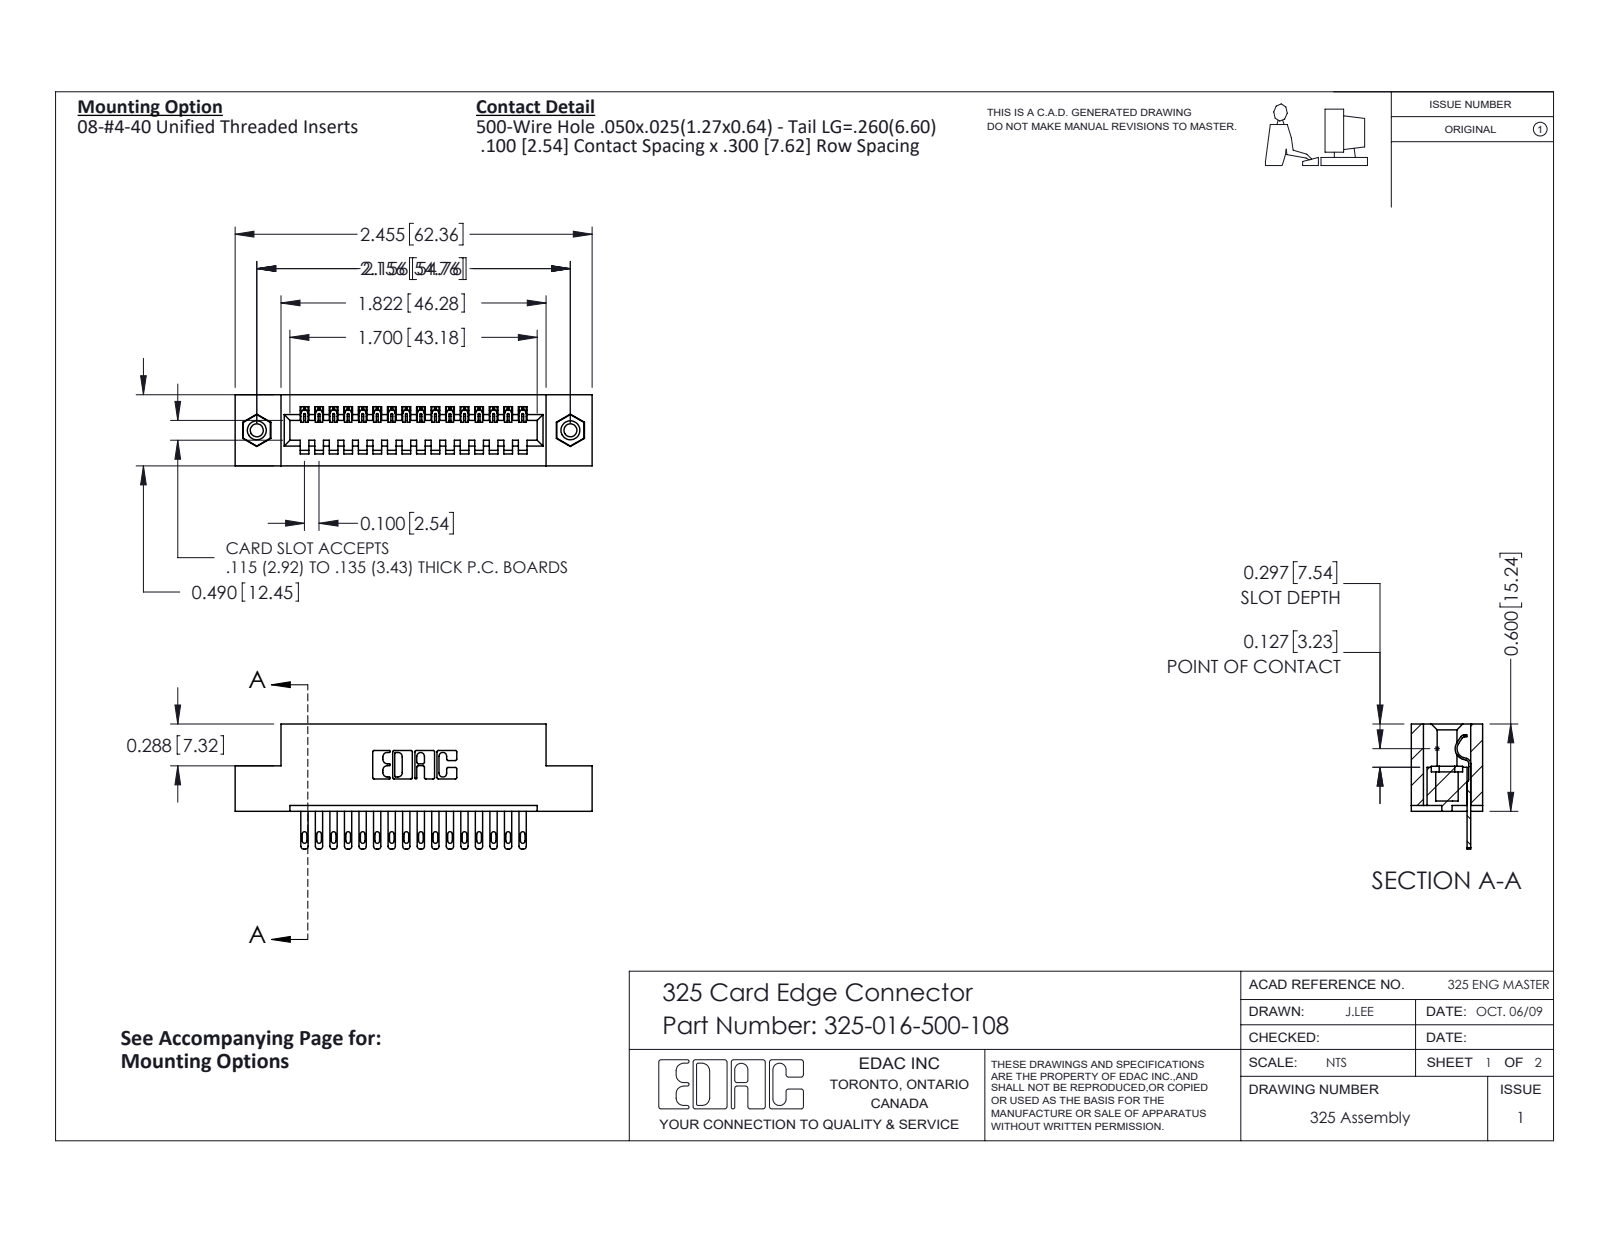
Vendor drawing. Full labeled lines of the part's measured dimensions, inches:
Part name (STEP PRODUCT): 325-016-500-108; 325 Part_TI; 345-250-001_345-250-003-102; 325-292-001_325-293-100
STEP written by: SolidWorks 2016 (CONFIG_CONTROL_DESIGN)
Units: inches
Bodies: 19 solids, 1038 faces (678 planar, 344 cylindrical, 16 other)
Overall size (bounding box): 2.455 × 0.86 × 0.49
Volume: 0.471 in³ · Surface area: 12.46 in²
Round holes (diameter × count): ⌀0.089 ×2, ⌀0.125 ×2, ⌀0.16 ×2
Round bosses / shafts (diameter × count): ⌀0.155 ×2
Partial cylindrical surfaces — rounded edges, fillets, slot ends (radius × count): R0.006 ×32, R0.016 ×32, R0.02 ×32, R0.01 ×22, R0.007 ×6, R0.031 ×6, R0.026 ×3, R0.014 ×1
Main face-to-face distances: 0.083, 0.407, 0.3, 0.49, 0.107, 0.383, 0.025, 0.04, 0.1, 0.6
Hole centre spacings: 2.156
